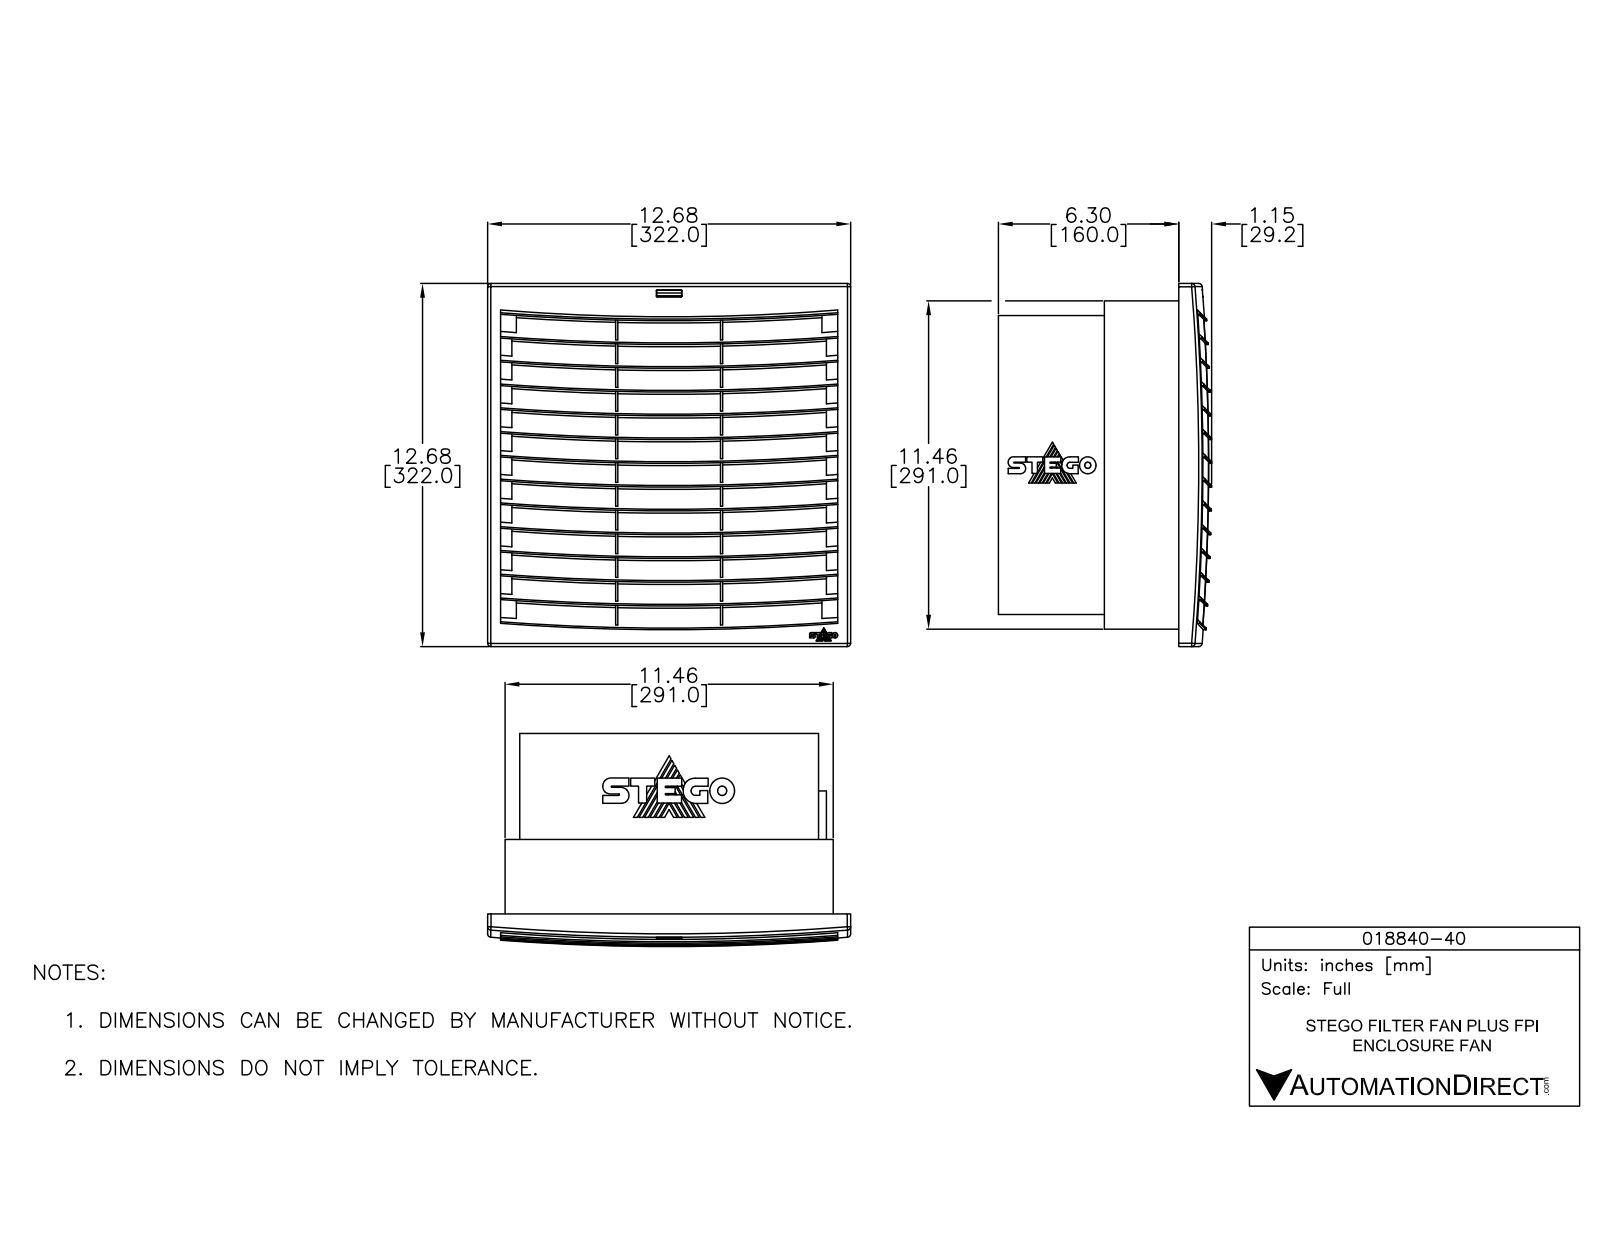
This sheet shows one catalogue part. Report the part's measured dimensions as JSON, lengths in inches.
{"part_name": "018840-40", "step_written_by": "SolidWorks 2018 (AUTOMOTIVE_DESIGN)", "units": "inches", "bodies": {"solids": 1, "faces": 831, "planar": 477, "cylindrical": 354, "other": 0}, "overall_size": [12.677, 12.677, 7.441], "volume_in3": 276.7, "surface_area_in2": 1385, "round_holes": [[3, 1], [3.99, 1], [4.692, 1], [4.979, 1], [5.909, 1], [5.969, 1], [6.958, 1], [7.126, 1], [7.947, 1], [8.344, 1], [9.134, 1], [9.738, 1]], "round_bosses_or_shafts": [[11.389, 1], [10.846, 1], [10.738, 1], [8.698, 1], [8.341, 1], [7.481, 1], [7.352, 1], [6.362, 1]], "partial_cylinders_radius": [[64.96, 23], [4.43, 7], [0.276, 4], [0.343, 4], [1.217, 1], [1.737, 1], [1.914, 1], [44.216, 1]], "face_to_face_distances": [0.636, 1.272, 1.909, 2.545, 0.197, 0.059, 3.181, 0.287, 11.17, 0.695]}
